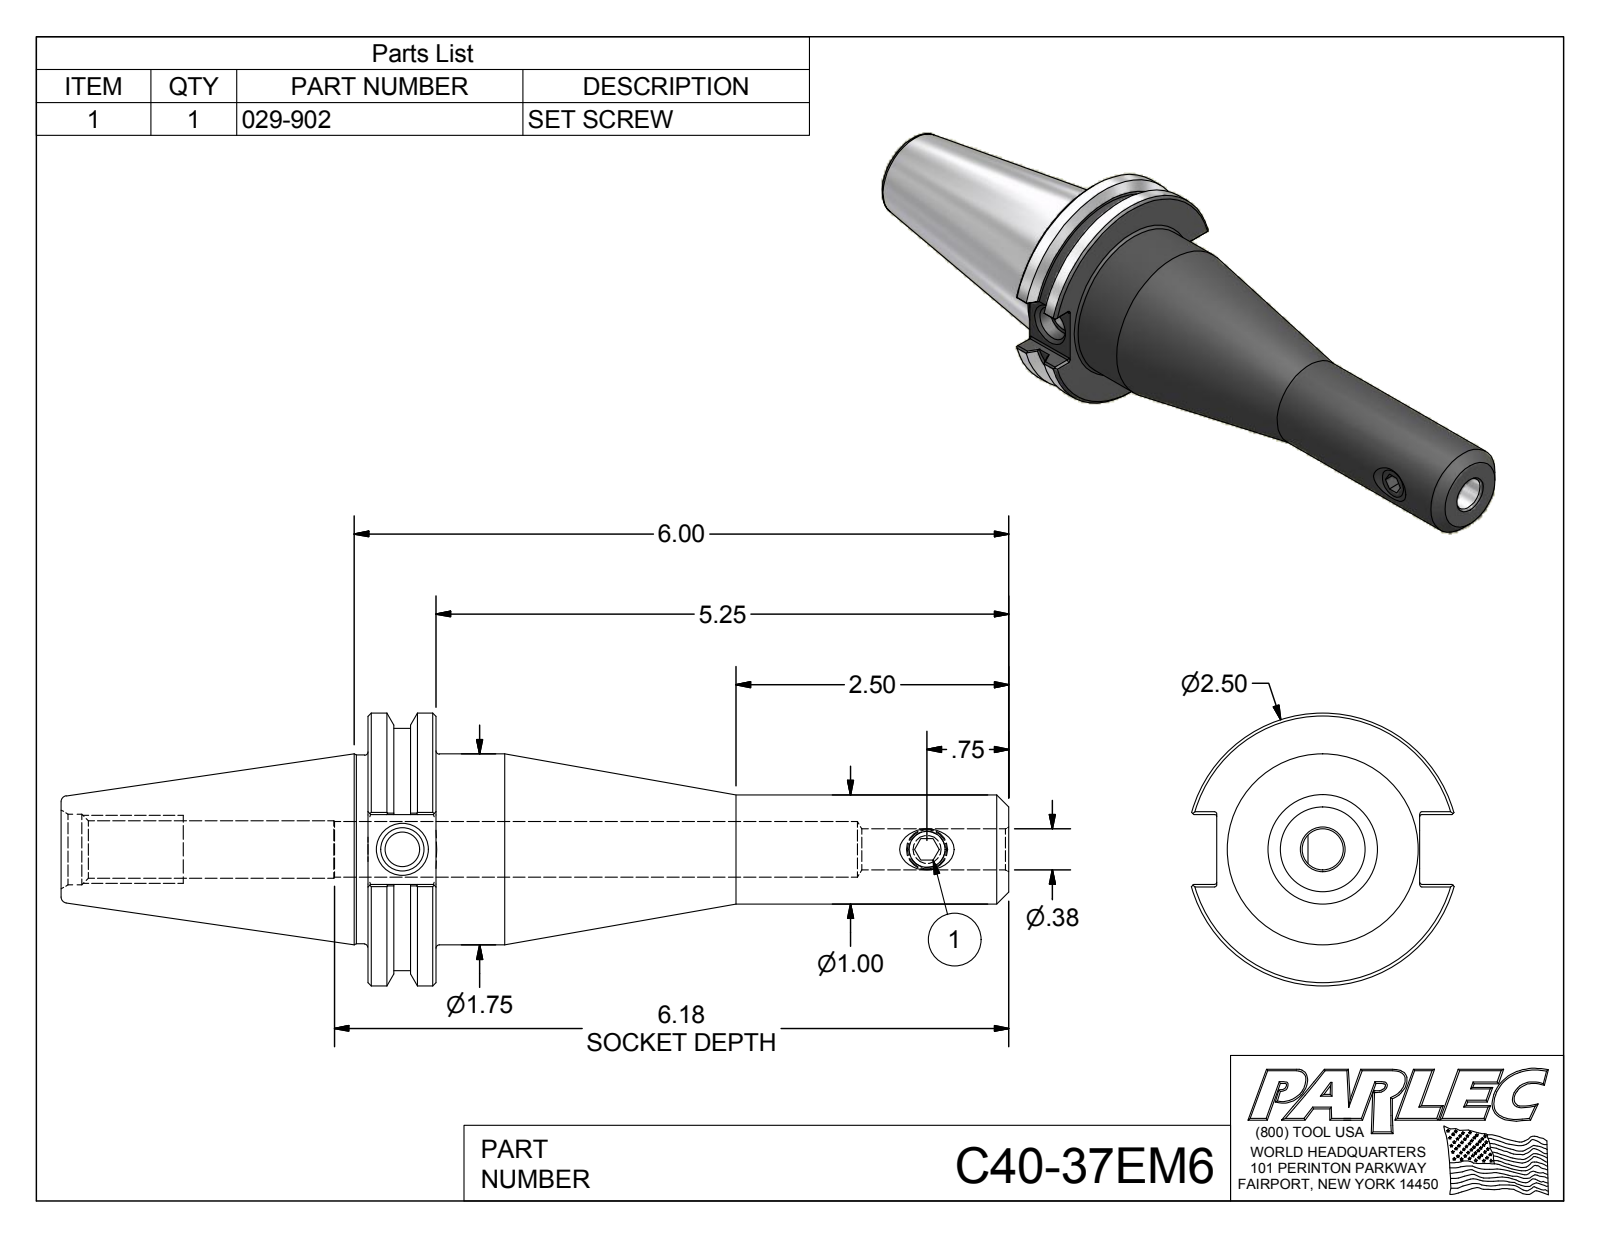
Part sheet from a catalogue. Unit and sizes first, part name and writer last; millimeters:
Units: millimetres
Overall size (bounding box): 220.6 × 63.5 × 61.1
Round holes (diameter × count): ⌀8 ×1, ⌀8.4 ×1, ⌀9.5 ×1, ⌀10.1 ×1, ⌀13 ×1, ⌀13.4 ×1, ⌀16.5 ×1
Round bosses / shafts (diameter × count): ⌀63.5 ×1, ⌀56.4 ×1, ⌀44.5 ×1, ⌀43.9 ×1, ⌀25.4 ×1, ⌀9.5 ×1
Partial cylindrical surfaces — rounded edges, fillets, slot ends (radius × count): R0.5 ×12
Main face-to-face distances: 15.9, 149.2, 133.4, 16.3, 6, 47.2, 71.4, 87.3, 220.6, 81.3
Hole centre spacings: 122.2
Volume: 194 700 mm³ · Surface area: 37 920 mm²
Bodies: 2 solids, 102 faces (40 planar, 29 cylindrical, 33 other)
Part name (STEP PRODUCT): C40-37EM6; C40-37EM6-1; 029-902
STEP written by: Autodesk Inventor 2012 (AUTOMOTIVE_DESIGN)
